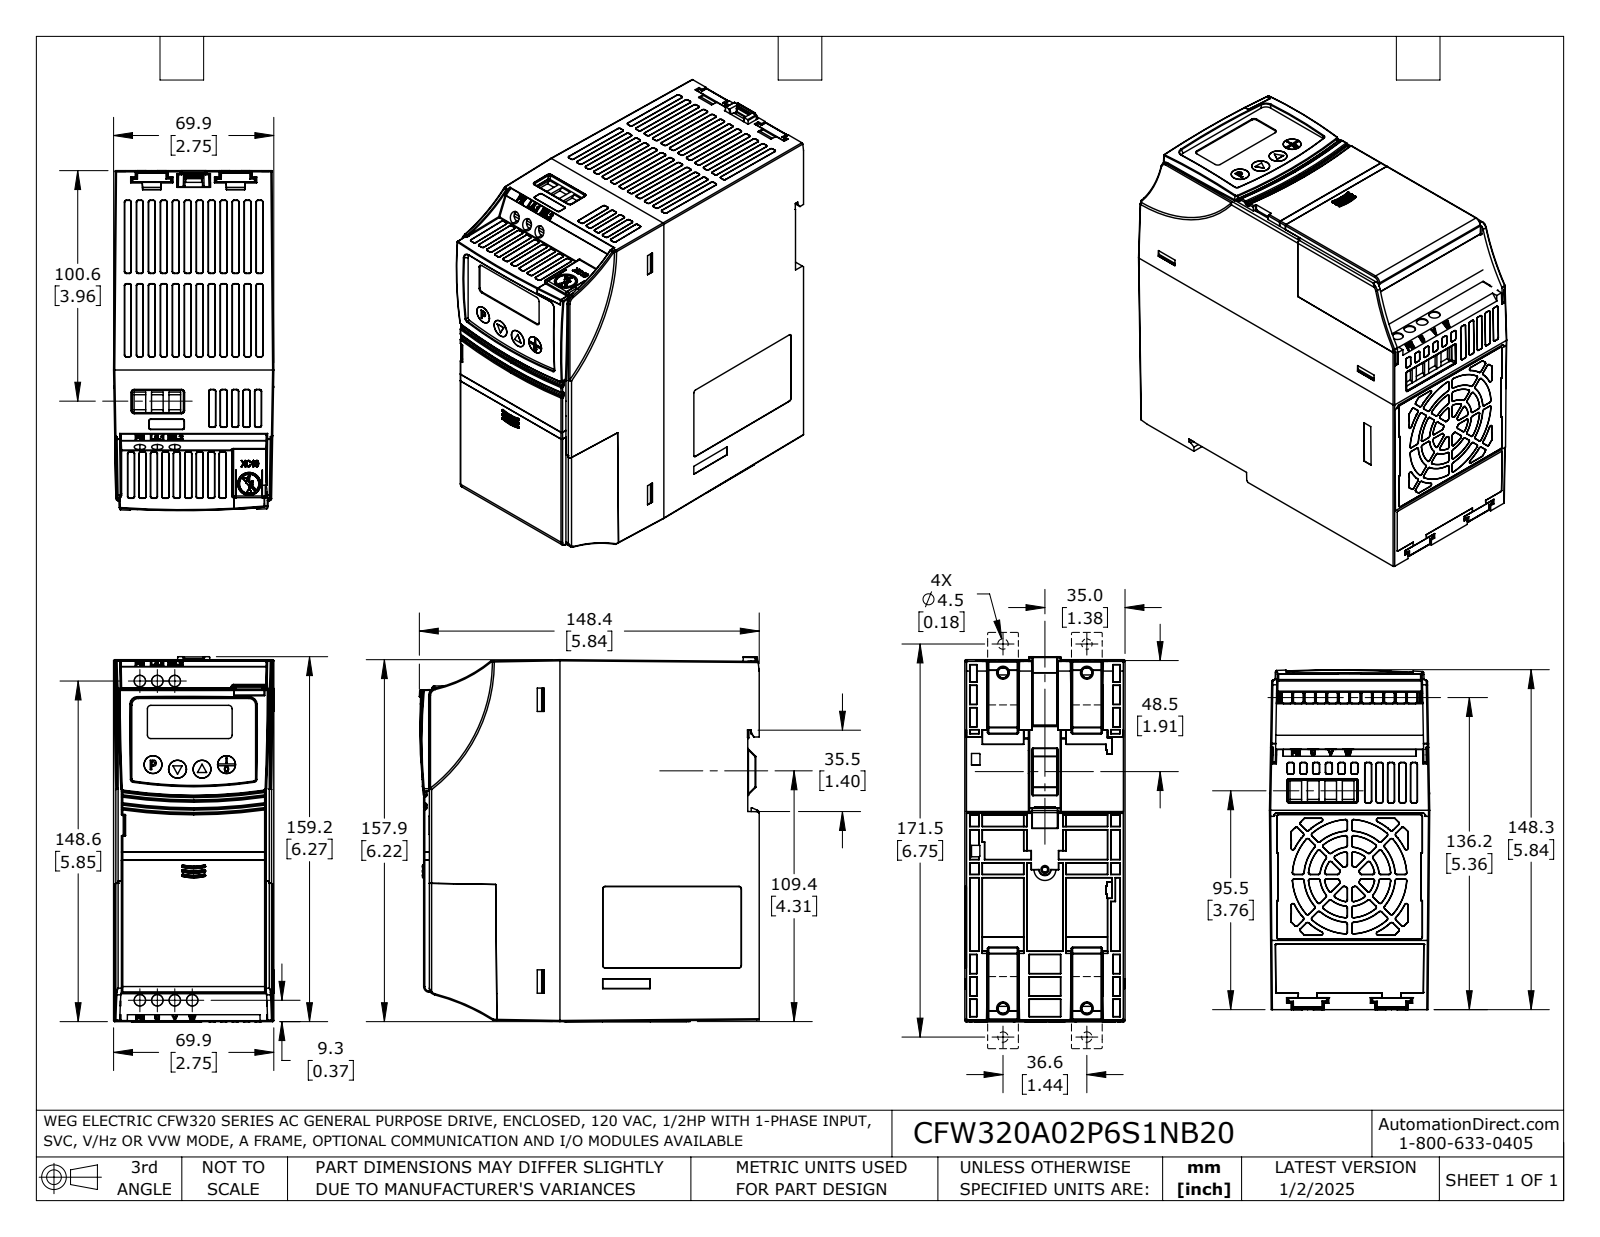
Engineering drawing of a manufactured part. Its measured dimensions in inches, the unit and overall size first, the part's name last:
Units: inches
Overall size (bounding box): 6.269 × 5.841 × 2.754
Round holes (diameter × count): ⌀0.197 ×3
Partial cylindrical surfaces — rounded edges, fillets, slot ends (radius × count): R0.012 ×327, R0.02 ×150, R0.039 ×13, R0.03 ×5, R0.118 ×3, R0.01 ×2, R0.098 ×1, R0.126 ×1
Main face-to-face distances: 0.07, 0.055, 0.019, 0.05, 6, 5.33, 5.275, 5.571, 5.516, 0.241
Hole centre spacings: 0.3, 0.6
Volume: 15.24 in³ · Surface area: 309 in²
Bodies: 6 solids, 3715 faces (1587 planar, 853 cylindrical, 1275 other)
Part name (STEP PRODUCT): CFW320A02P6S1NB20
STEP written by: SolidWorks 2021 (AUTOMOTIVE_DESIGN)
